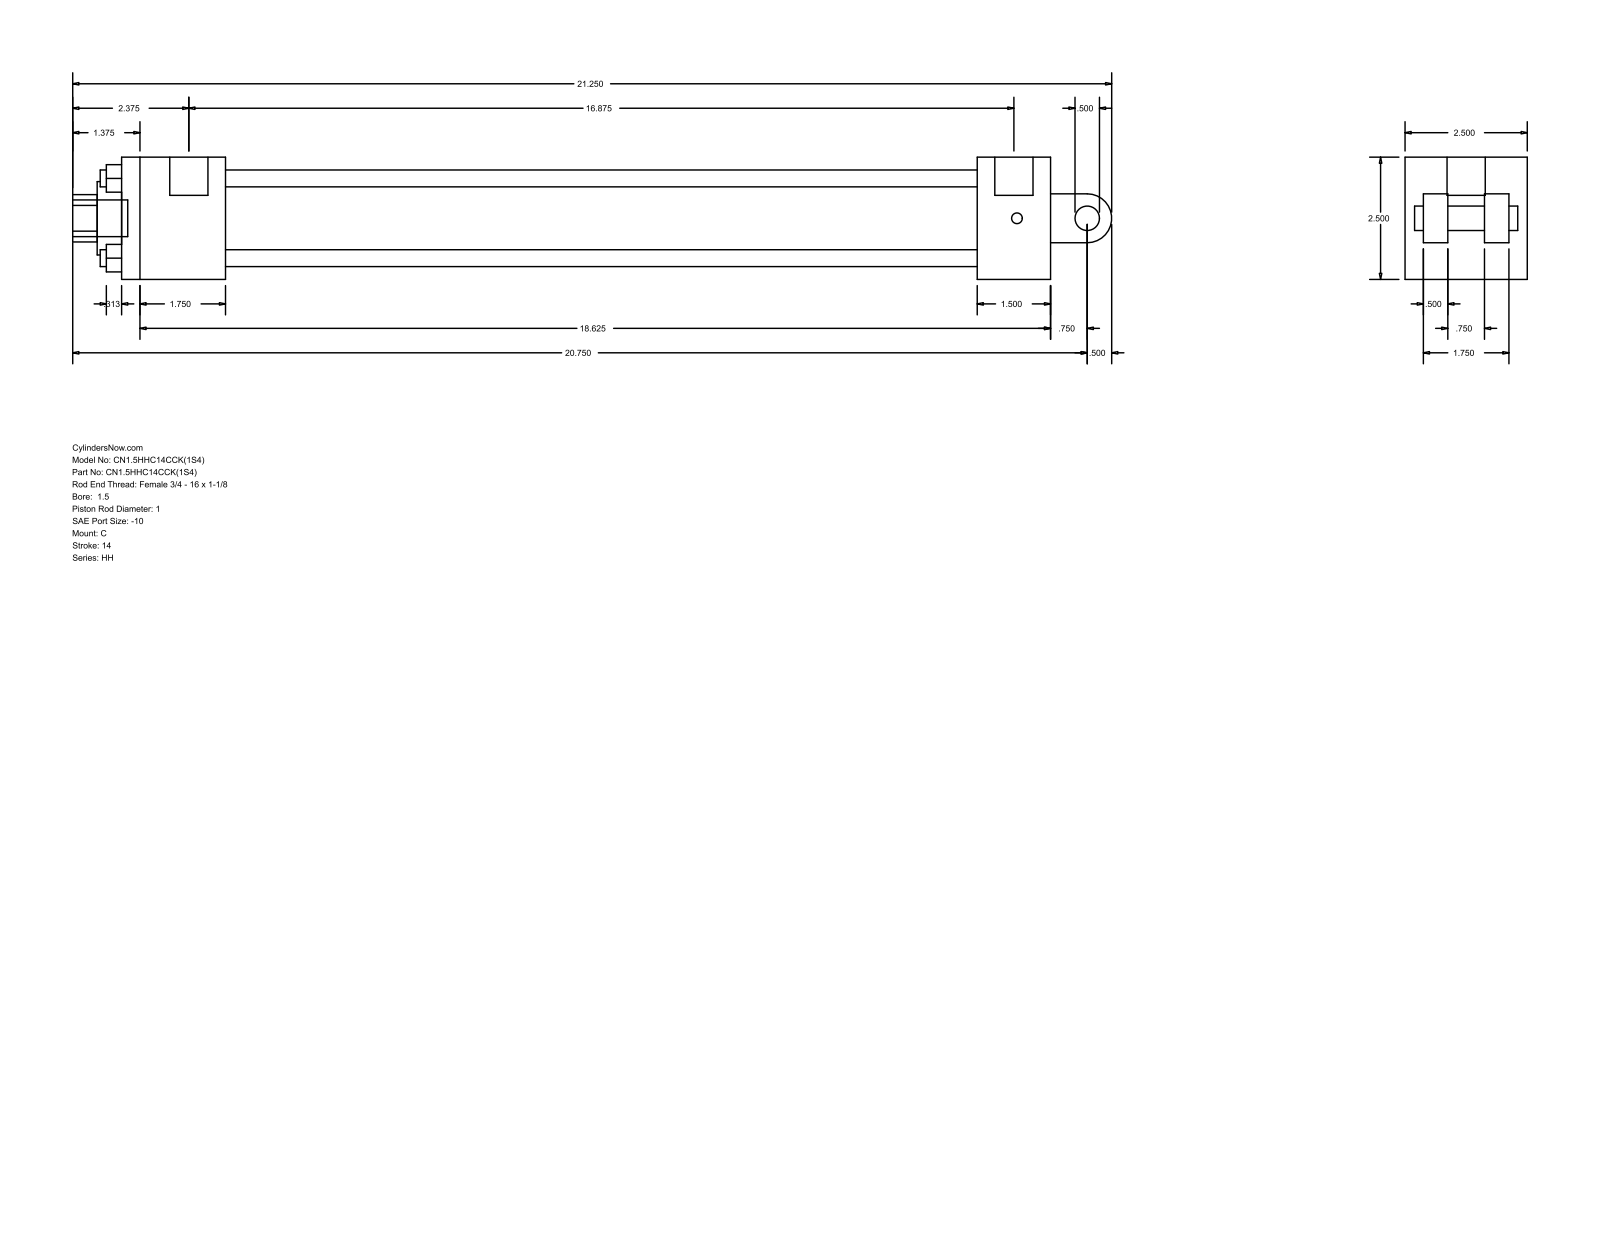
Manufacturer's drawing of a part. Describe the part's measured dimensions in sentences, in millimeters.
The part is named "HH_C__0150_1". Its 3-D file was written by "GSSL Pune (CONFIG_CONTROL_DESIGN)". It is 0 solids with 99 faces: 70 planar, 29 cylindrical and 0 other. Overall it measures 539.75 by 63.5 by 63.5 millimeters. Round holes: 4 of diameter 8.76, 2 of diameter 5.56, 1 of diameter 19.84, 1 of diameter 25.4, 1 of diameter 38.1, 1 of diameter 44.45. Round bosses or shafts: 2 of diameter 5.56, 1 of diameter 19.84, 1 of diameter 19.05, 1 of diameter 12.7. Partial cylindrical surfaces (rounded edges, fillets, slot ends): 1 of radius 12.29, 1 of radius 12.7. The main face-to-face distances are 63.5, 53.98, 390.52, 428.62, 38.1, 444.5, 482.6, 12.7, 9.52, 22.22. The hole center spacings are 29.27, 41.4, 58.55, 1.59.
